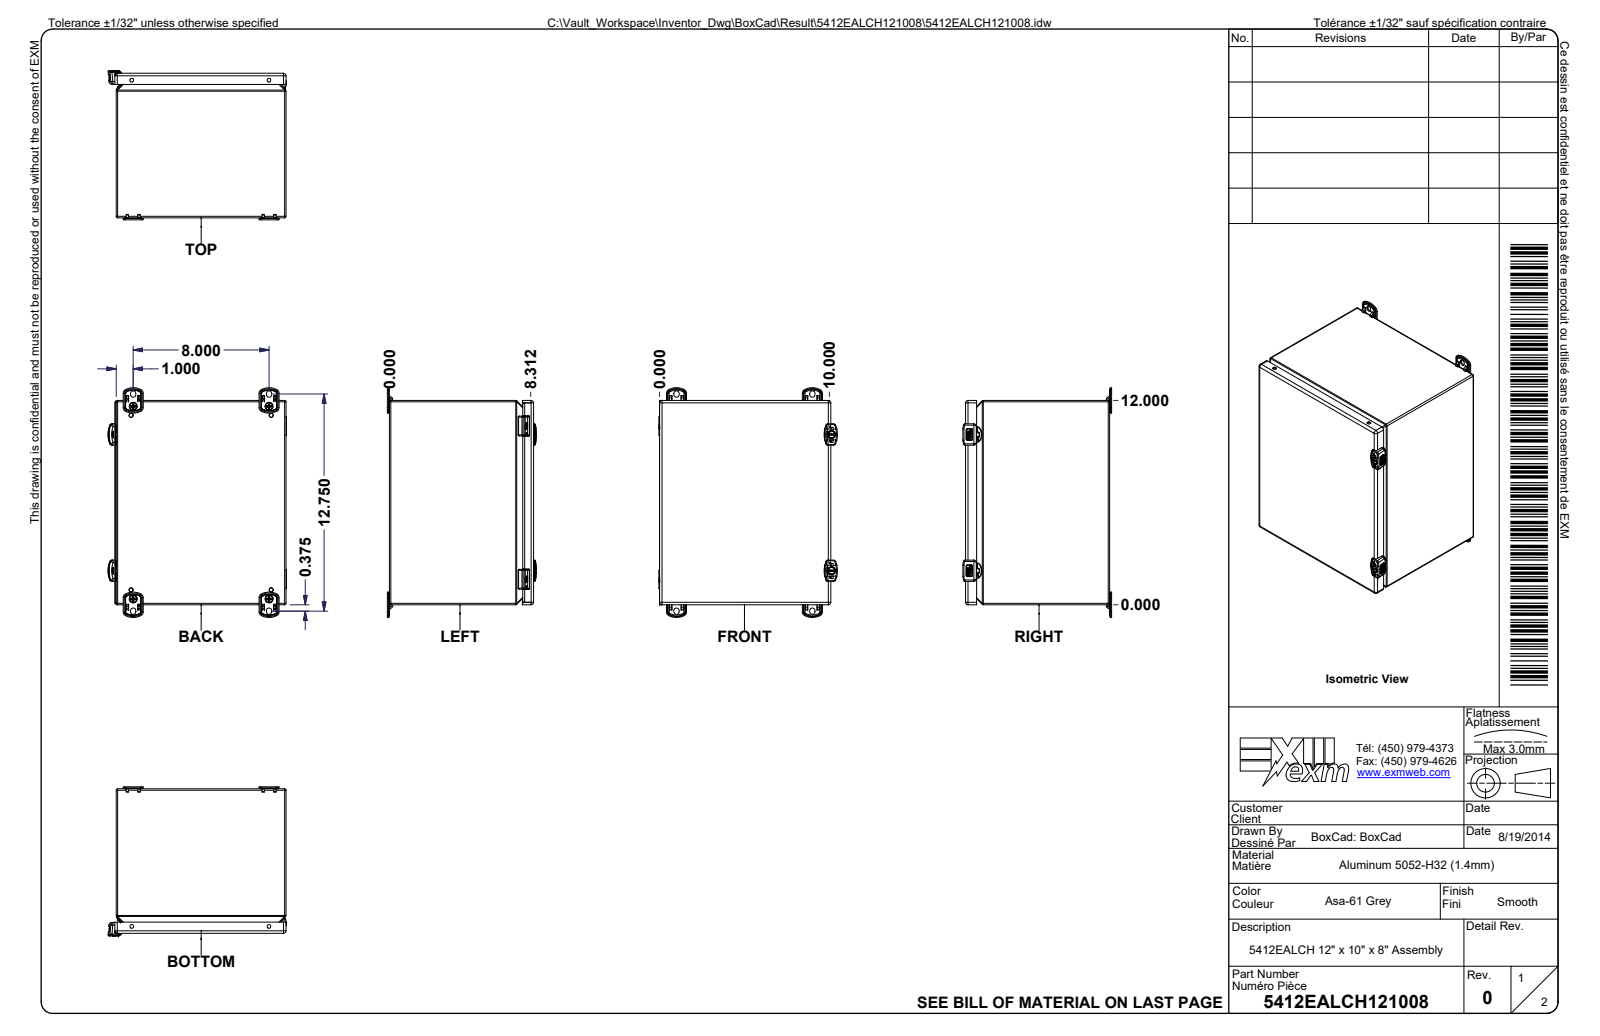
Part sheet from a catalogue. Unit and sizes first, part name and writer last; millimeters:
Units: millimetres
Overall size (bounding box): 342.8 × 266.8 × 222.5
Round holes (diameter × count): ⌀4.2 ×4, ⌀4.4 ×4, ⌀5 ×4, ⌀5 ×4, ⌀6 ×4, ⌀6 ×4, ⌀8.1 ×4, ⌀0.8 ×2, ⌀4.4 ×2, ⌀5.1 ×2, ⌀6.1 ×2, ⌀8.6 ×2
Round bosses / shafts (diameter × count): ⌀5.9 ×8, ⌀12.7 ×4, ⌀7.6 ×4, ⌀6 ×4, ⌀4.9 ×4, ⌀5 ×3, ⌀10.5 ×2, ⌀10 ×2
Partial cylindrical surfaces — rounded edges, fillets, slot ends (radius × count): R0.5 ×257, R0.3 ×209, R1 ×92, R0.1 ×64, R0.2 ×60, R1.5 ×57, R0.8 ×35, R0.1 ×33
Main face-to-face distances: 1.3, 252.7, 303.5, 1.3, 214.2, 212.9, 215.5, 214.2, 6, 7.7
Hole centre spacings: 203.2, 342.9, 13.9, 206.8, 273.8, 228.6, 209.6, 209.6
Volume: 732 700 mm³ · Surface area: 1 034 000 mm²
Bodies: 59 solids, 8409 faces (3583 planar, 2002 cylindrical, 2824 other)
Part name (STEP PRODUCT): 5412EALCH121008; 5412EALCH121008B; 5412EALCH121008B-P; STK-A-70469-1 (+8 more)
STEP written by: Autodesk Inventor 2020 (AUTOMOTIVE_DESIGN)
